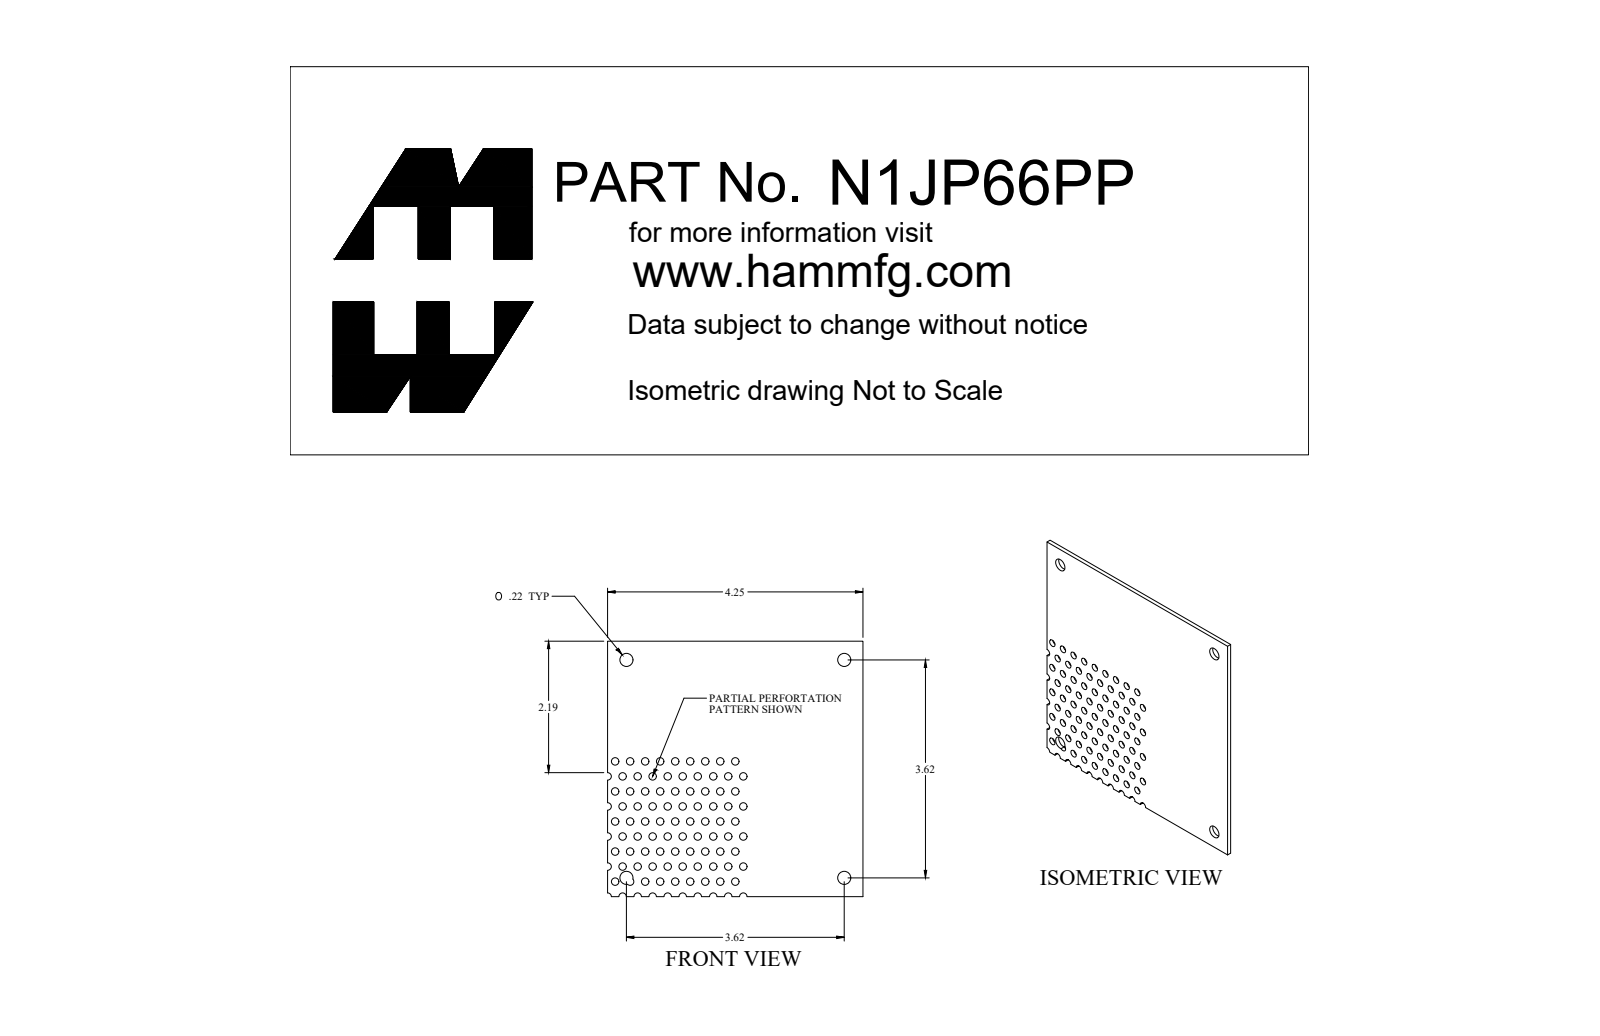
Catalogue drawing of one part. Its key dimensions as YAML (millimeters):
part_name: "N1JP66PP"
step_written_by: "SolidWorks 2018 (AUTOMOTIVE_DESIGN)"
units: millimeters
bodies: {solids: 1, faces: 203, planar: 19, cylindrical: 184, other: 0}
overall_size: [108, 108, 1.8]
volume: 19880
surface_area: 24150
round_holes:
  - {diameter: 3.2, count: 62}
  - {diameter: 3.2, count: 18}
  - {diameter: 5.5, count: 4}
partial_cylinders:
  - {radius: 1.6, count: 13}
  - {radius: 1.6, count: 2}
face_to_face_distances: [1.8, 108]
hole_center_spacings: [12.7, 7.1, 6.4, 14.2, 18, 11.4, 17.1, 19.1]
